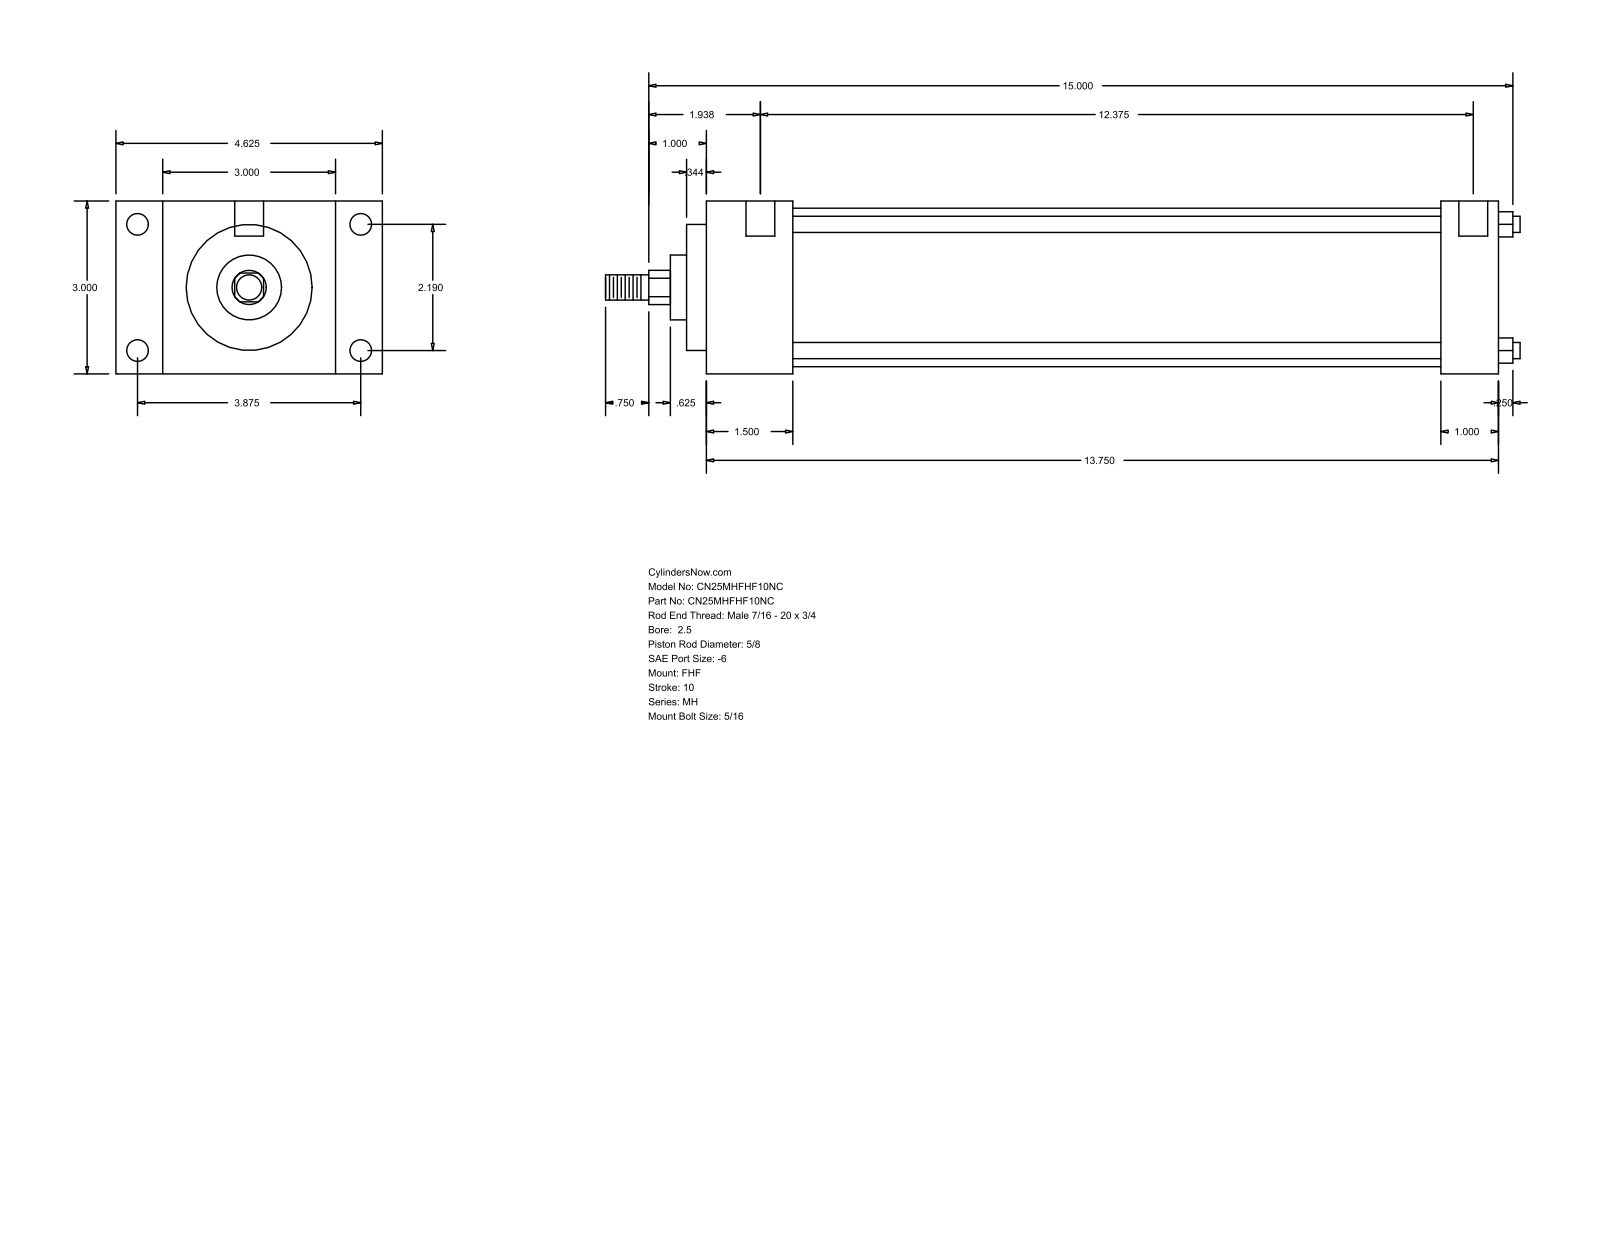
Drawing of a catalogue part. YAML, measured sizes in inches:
part_name: "MH_FHF__0250_0.625"
step_written_by: "GSSL Pune (CONFIG_CONTROL_DESIGN)"
units: inches
bodies: {solids: 0, faces: 90, planar: 61, cylindrical: 29, other: 0}
overall_size: [15.875, 4.625, 3]
round_holes:
  - {diameter: 0.219, count: 4}
  - {diameter: 0.375, count: 4}
  - {diameter: 0.5, count: 2}
round_bosses_or_shafts:
  - {diameter: 0.281, count: 4}
  - {diameter: 2.75, count: 1}
  - {diameter: 2.187, count: 1}
  - {diameter: 1.125, count: 1}
  - {diameter: 0.625, count: 1}
  - {diameter: 0.437, count: 1}
partial_cylinders:
  - {radius: 0.297, count: 1}
face_to_face_distances: [3, 13.75, 1.5, 12.25, 0.813, 3.813, 4.625, 1, 12.75, 11.25]
hole_center_spacings: [2.19, 3.875, 4.451, 12.687, 0.125, 0.187, 12.375, 12.5]
